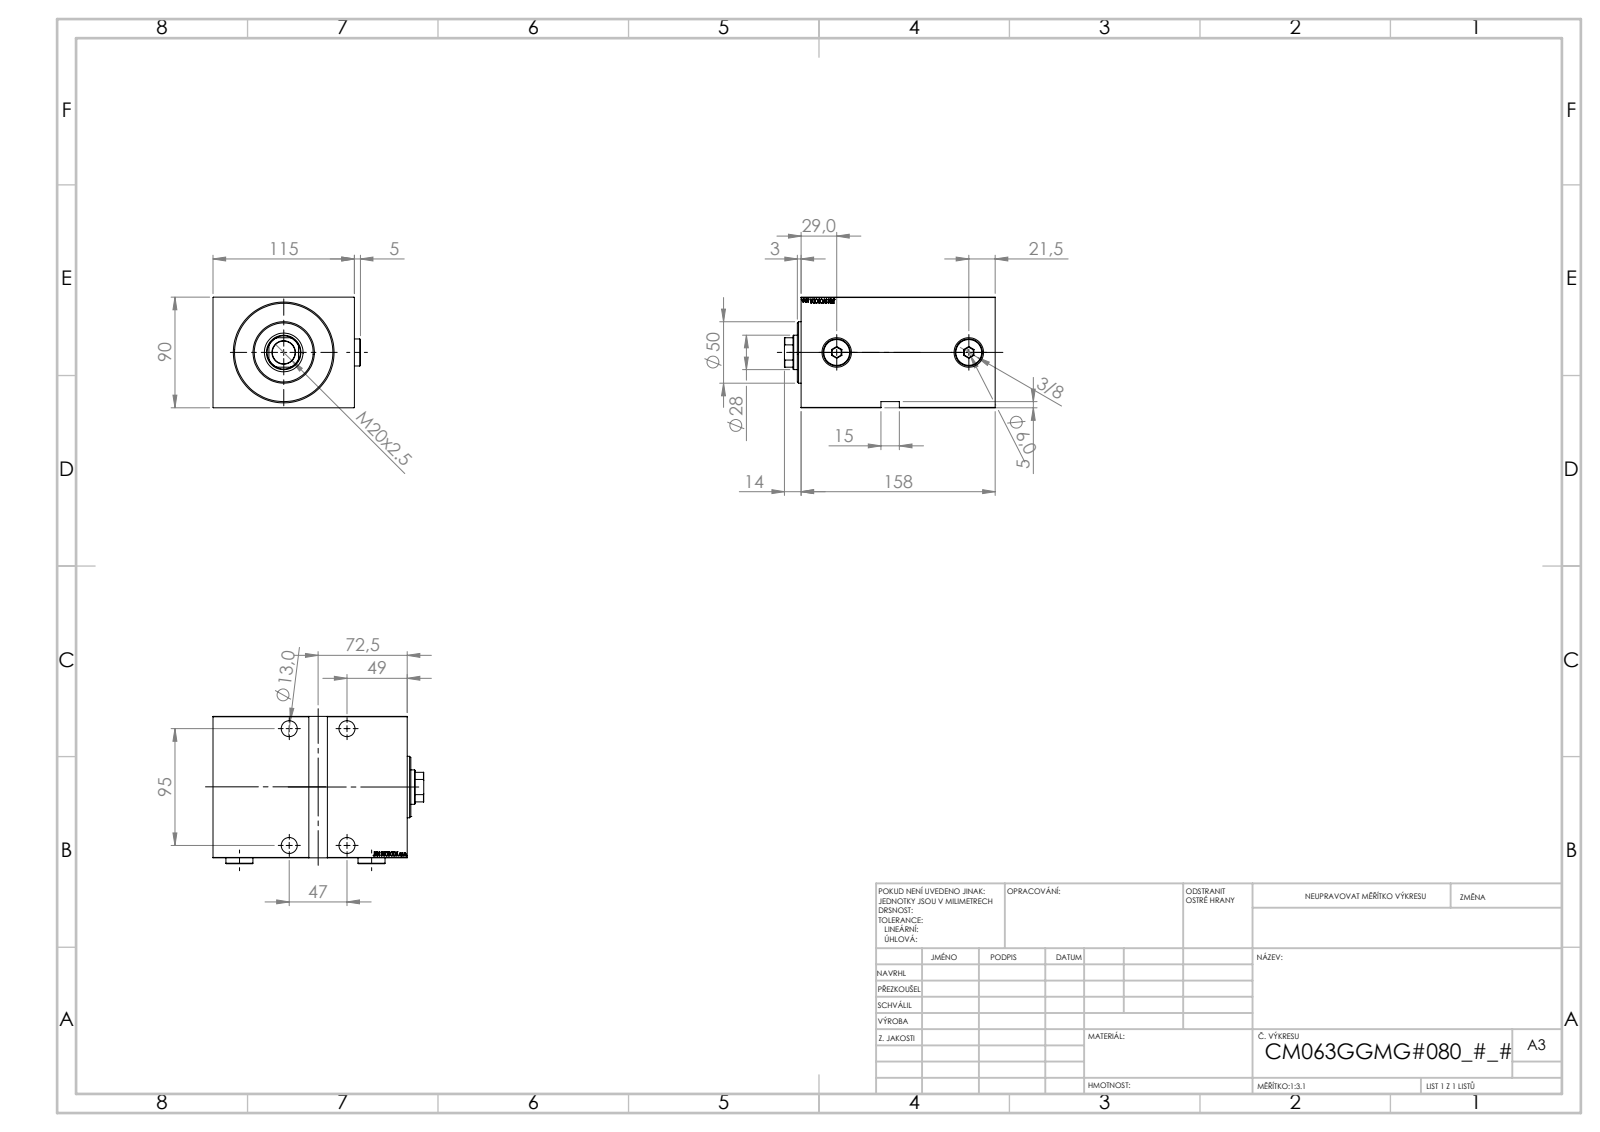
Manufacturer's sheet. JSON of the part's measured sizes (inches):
{"part_name": "Zatka_OIL_PORT; V450CM_G_Body; V450CM_G_VCP; V450CM_VC_G", "step_written_by": "SolidWorks 2019 (CONFIG_CONTROL_DESIGN)", "units": "inches", "bodies": {"solids": 5, "faces": 896, "planar": 442, "cylindrical": 56, "other": 398}, "overall_size": [6.752, 4.72, 3.543], "volume_in3": 81.95, "surface_area_in2": 265.7, "round_holes": [[0.512, 4], [0.748, 4], [0.236, 2], [0.637, 2], [0.945, 2], [0.728, 1], [1.102, 1], [1.24, 1], [2.48, 1], [2.559, 1], [3.15, 1]], "round_bosses_or_shafts": [[0.866, 2], [1.969, 1]], "partial_cylinders_radius": [[0.531, 1]], "face_to_face_distances": [3.543, 4.528, 0.197, 6.22, 0.689, 5.531, 6.024, 5.335, 3.681, 2.539], "hole_center_spacings": [1.85, 3.74, 4.173, 4.232]}
